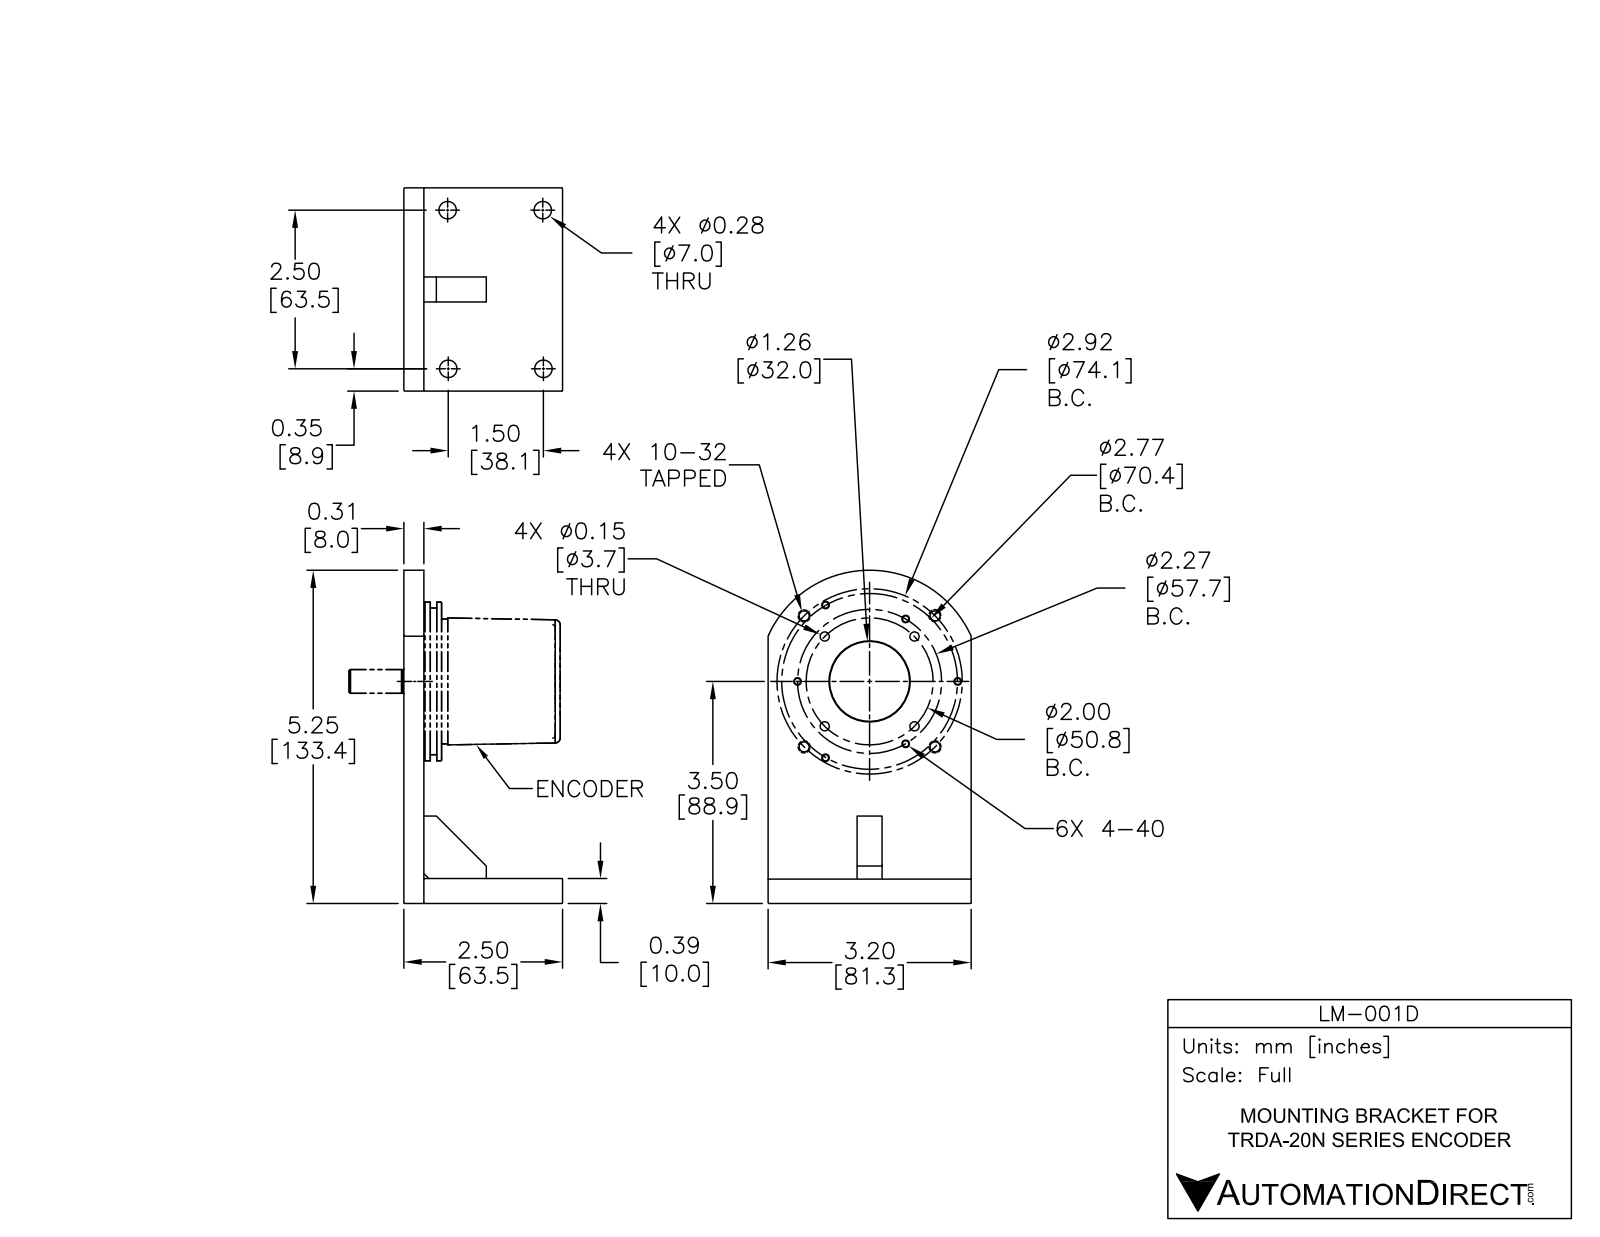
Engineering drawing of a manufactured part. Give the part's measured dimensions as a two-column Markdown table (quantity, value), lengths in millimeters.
| quantity | value |
| --- | --- |
| part name | HXM3-8; LM-001D; L-2C; L-2B (+1 more) |
| STEP written by | SolidWorks 2016 (AUTOMOTIVE_DESIGN) |
| units | millimeters |
| bodies | 7 solids, 205 faces (89 planar, 80 cylindrical, 36 other) |
| overall size | 133.4 × 81.3 × 63.5 |
| volume | 119 959 mm³ |
| surface area | 39 072 mm² |
| round holes (diameter × count) | 2.26 × 6, 3.2 × 4, 3.7 × 4, 5.54 × 4, 7.1 × 4, 3.5 × 3, 6.3 × 3, 6 × 1, 32 × 1 |
| round bosses / shafts (diameter × count) | 5.5 × 4, 3 × 4 |
| partial cylindrical surfaces (radius × count) | 44.5 × 1 |
| main face-to-face distances | 8, 10, 7.7, 81.3, 35.65, 45.65, 63.5, 55.8, 55.5, 3 |
| hole center spacings | 44.92, 32.49, 11.65, 25.4, 35.92, 37.05, 52.4, 60.97 |
